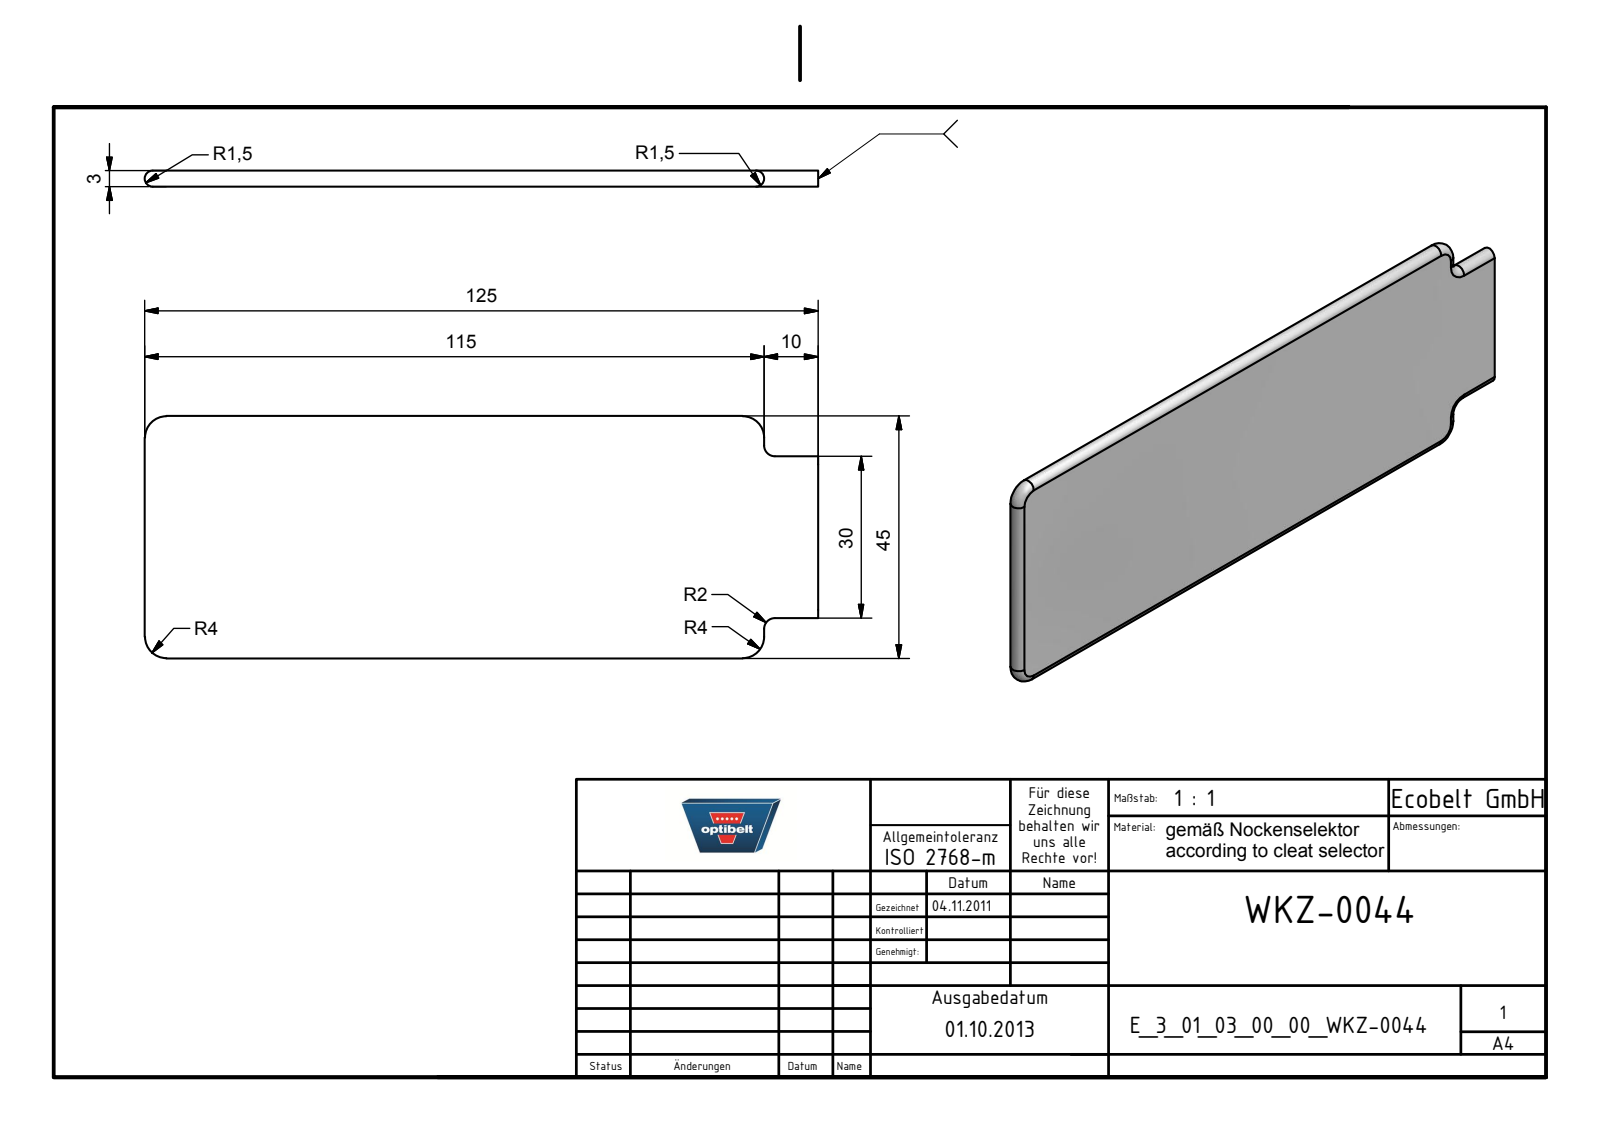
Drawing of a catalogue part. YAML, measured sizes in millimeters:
part_name: "E_3_01_03_00_00_WKZ-0044"
step_written_by: "Autodesk Inventor 2025 (AUTOMOTIVE_DESIGN)"
units: millimeters
bodies: {solids: 1, faces: 16, planar: 3, cylindrical: 7, other: 6}
overall_size: [125, 45, 3]
volume: 16099
surface_area: 11529
partial_cylinders:
  - {radius: 1.5, count: 6}
face_to_face_distances: [3]
